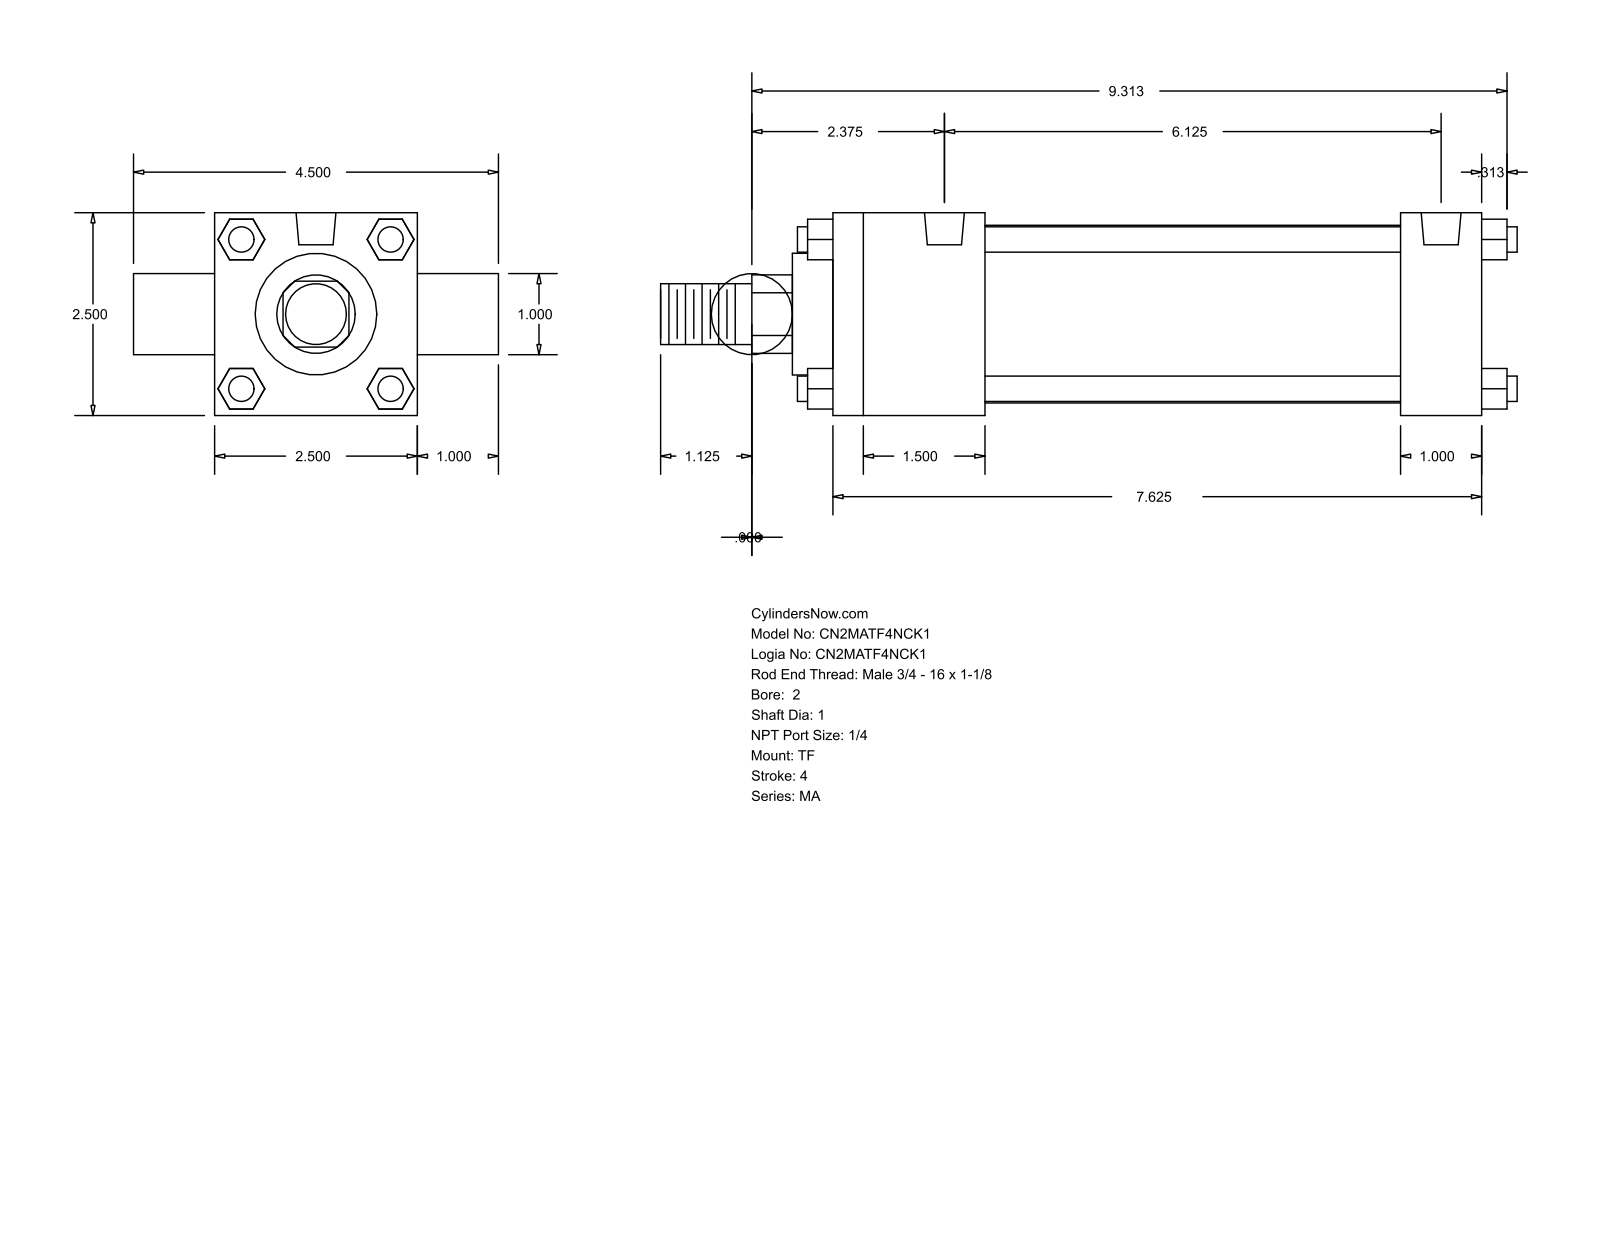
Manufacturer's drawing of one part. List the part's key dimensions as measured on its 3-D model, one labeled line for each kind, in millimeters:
Part name (STEP PRODUCT): MA_TF__0200_1
STEP written by: GSSL Pune (CONFIG_CONTROL_DESIGN)
Units: millimetres
Bodies: 0 solids, 120 faces (92 planar, 28 cylindrical, 0 other)
Overall size (bounding box): 268.29 × 114.3 × 63.5
Round holes (diameter × count): ⌀7.94 ×3, ⌀12.49 ×2
Round bosses / shafts (diameter × count): ⌀7.94 ×4, ⌀25.4 ×2, ⌀55.63 ×1, ⌀38.1 ×1, ⌀19.05 ×1
Partial cylindrical surfaces — rounded edges, fillets, slot ends (radius × count): R12.29 ×1
Main face-to-face distances: 63.5, 25.4, 203.2, 12.7, 47.63, 177.8, 130.17, 155.57, 88.9, 23.37
Hole centre spacings: 155.57
